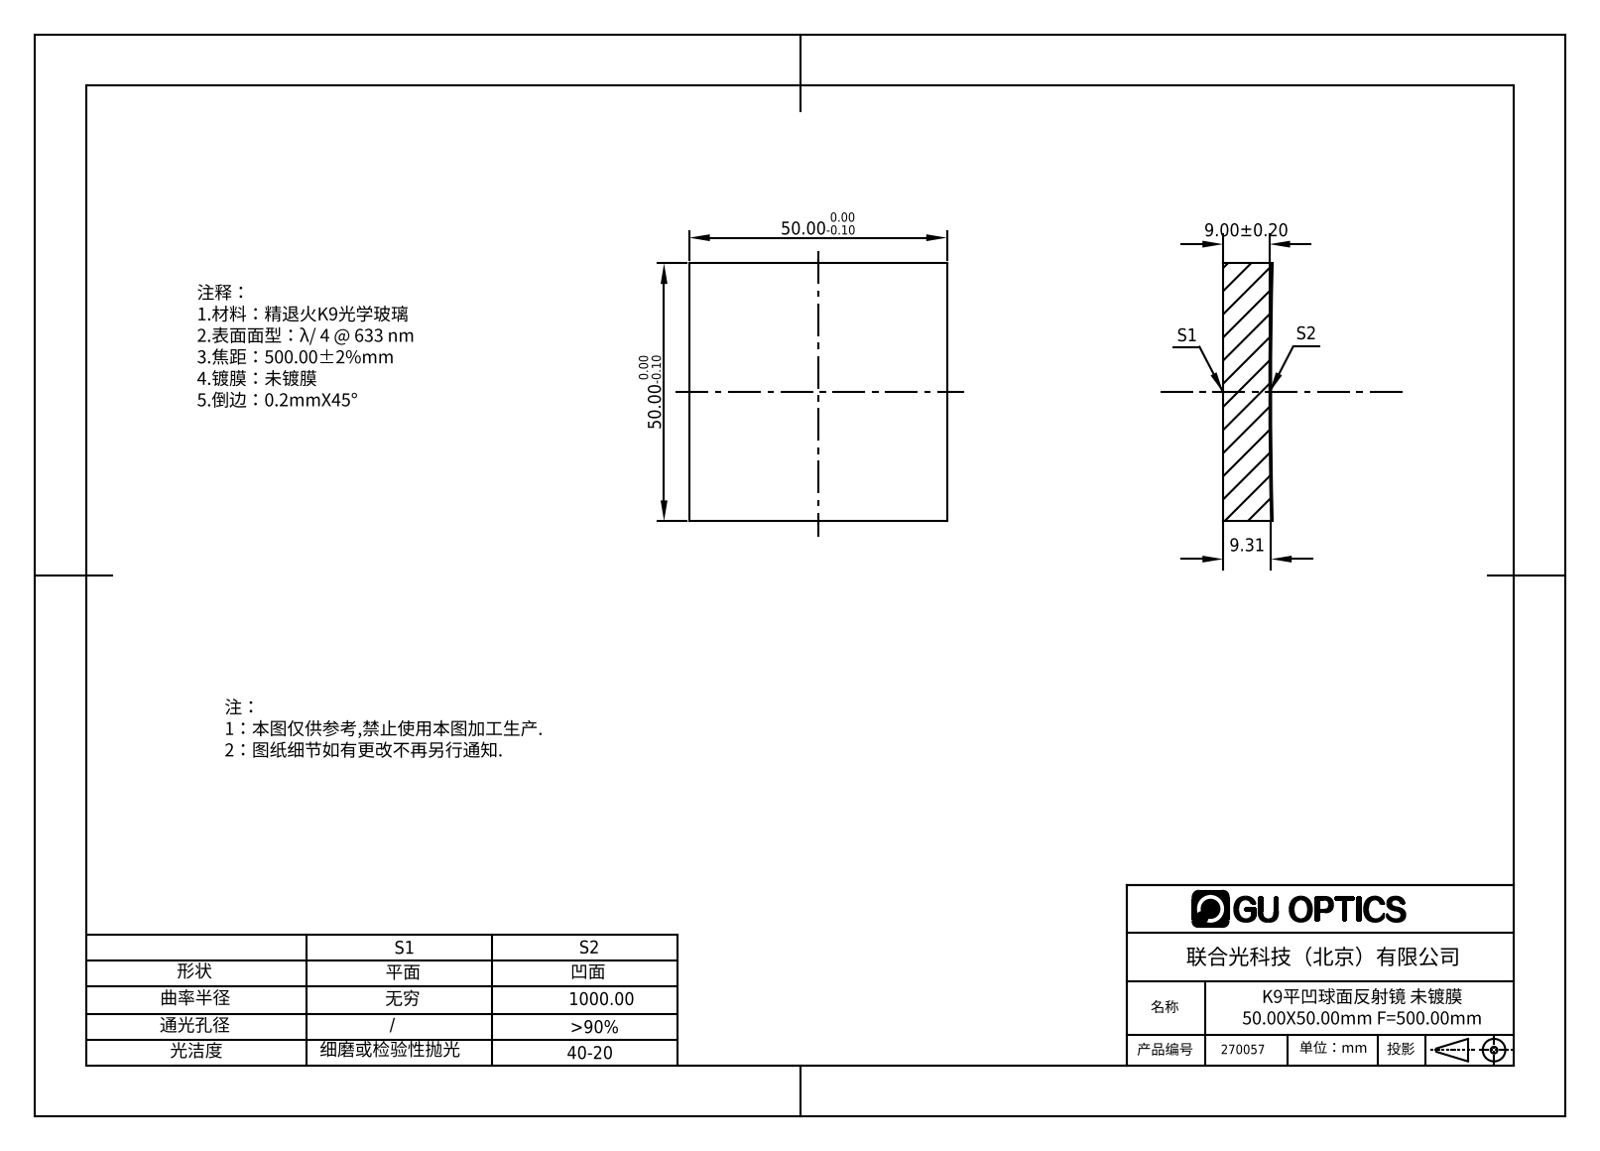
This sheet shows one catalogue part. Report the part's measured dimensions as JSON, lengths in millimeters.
{"part_name": "270057", "step_written_by": "SolidWorks 2019 (AUTOMOTIVE_DESIGN)", "units": "millimeters", "bodies": {"solids": 1, "faces": 7, "planar": 5, "cylindrical": 0, "other": 2}, "overall_size": [50, 50, 9.62], "volume_mm3": 23021, "surface_area_mm2": 6884, "face_to_face_distances": [50]}
